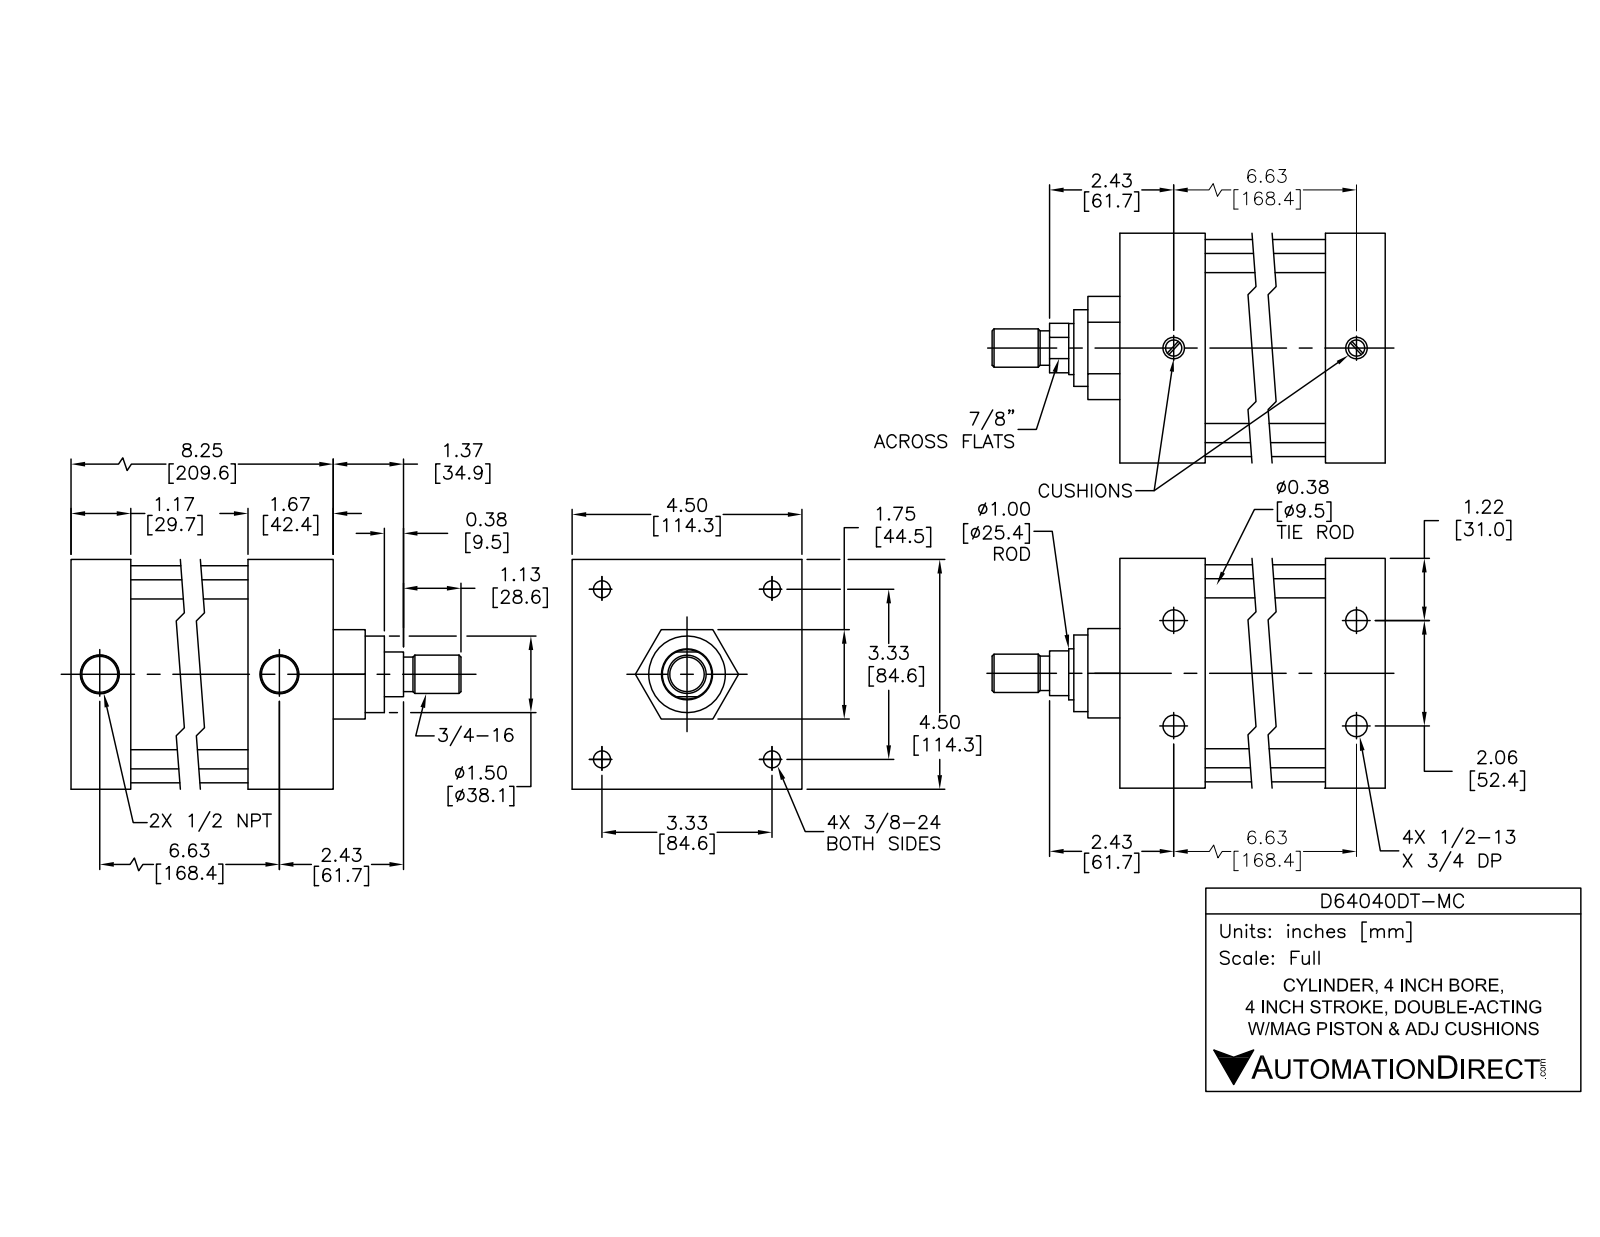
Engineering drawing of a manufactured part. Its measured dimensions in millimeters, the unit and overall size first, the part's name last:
Units: millimetres
Overall size (bounding box): 272.9 × 114.3 × 114.3
Round holes (diameter × count): ⌀8.4 ×4, ⌀10.3 ×4, ⌀10.6 ×4, ⌀15.9 ×4, ⌀12.7 ×2, ⌀19.5 ×2, ⌀25.4 ×1, ⌀25.5 ×1, ⌀101.6 ×1
Round bosses / shafts (diameter × count): ⌀15.5 ×4, ⌀9.5 ×4, ⌀8.6 ×4, ⌀108 ×1, ⌀101.5 ×1, ⌀44.5 ×1, ⌀25.3 ×1, ⌀24.6 ×1
Partial cylindrical surfaces — rounded edges, fillets, slot ends (radius × count): R11.4 ×4
Main face-to-face distances: 114.3, 2, 135.3, 209.4, 44.5, 177.7, 31.7, 146.1, 31.6, 63.4
Hole centre spacings: 84.4, 170.2, 168.2, 26.2, 26.2, 52.4, 59.7, 119.3
Volume: 1 449 000 mm³ · Surface area: 273 400 mm²
Bodies: 12 solids, 303 faces (99 planar, 114 cylindrical, 90 other)
Part name (STEP PRODUCT): D64040DT-MC; D64040DT-M PISTON; D64040DT-M BODY
STEP written by: SolidWorks 2015 (AUTOMOTIVE_DESIGN)
